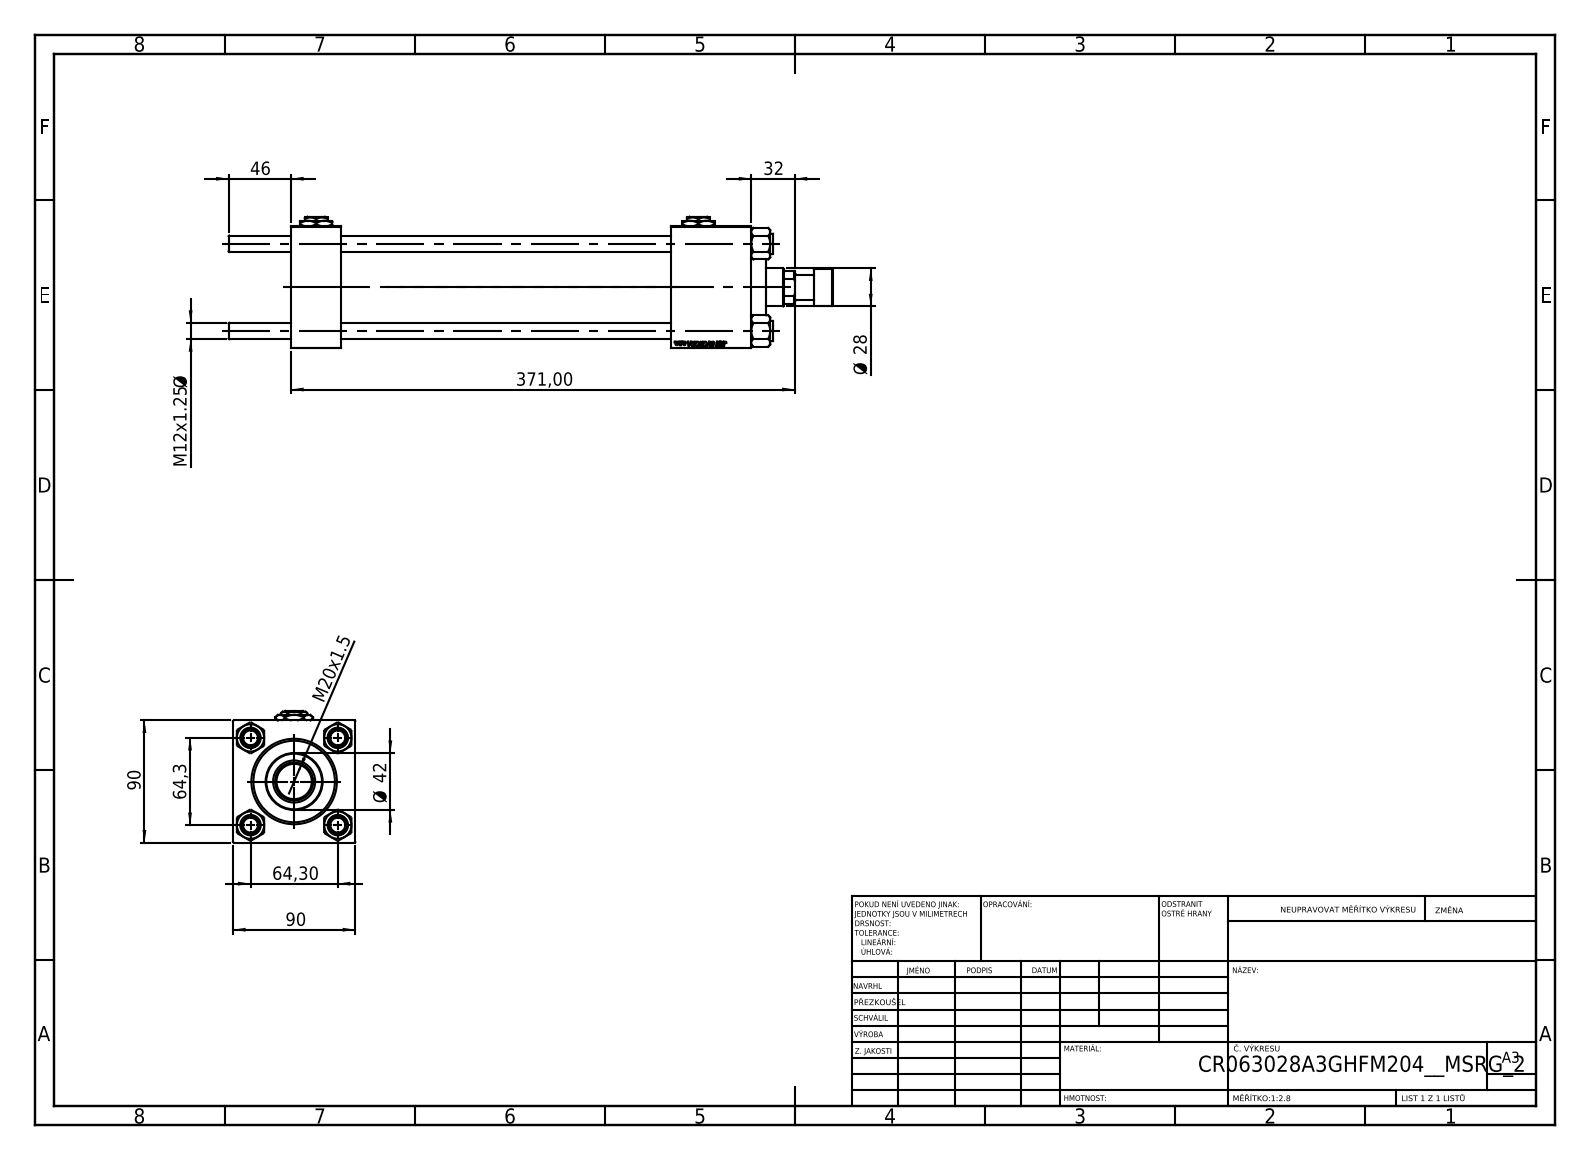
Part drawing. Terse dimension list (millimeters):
name: V215CR_ROD_END_F; CR025_012_A_0_G_A_G_M_020_+#_##_TYCINKA; V215_VC_A; V215CR_VCP (+3 more)
written by: SolidWorks 2019 (CONFIG_CONTROL_DESIGN)
unit: mm
bodies: 14 solids, 1247 faces (571 planar, 92 cylindrical, 584 other)
size: 445 × 97 × 90
volume: 1 297 000 mm³; area: 323 542 mm²
holes: 4× ⌀12, 2× ⌀7, 2× ⌀20.96, 2× ⌀30, 1× ⌀18.5, 1× ⌀28, 1× ⌀31, 1× ⌀50, 1× ⌀60, 1× ⌀63
bosses: 4× ⌀15, 1× ⌀69, 1× ⌀42, 1× ⌀27, 1× ⌀18
face distances: 90, 37, 339, 302, 59, 280, 243, 310.3, 273.3, 30.3
hole spacings: 45.47, 64.3, 90.93, 281.5
